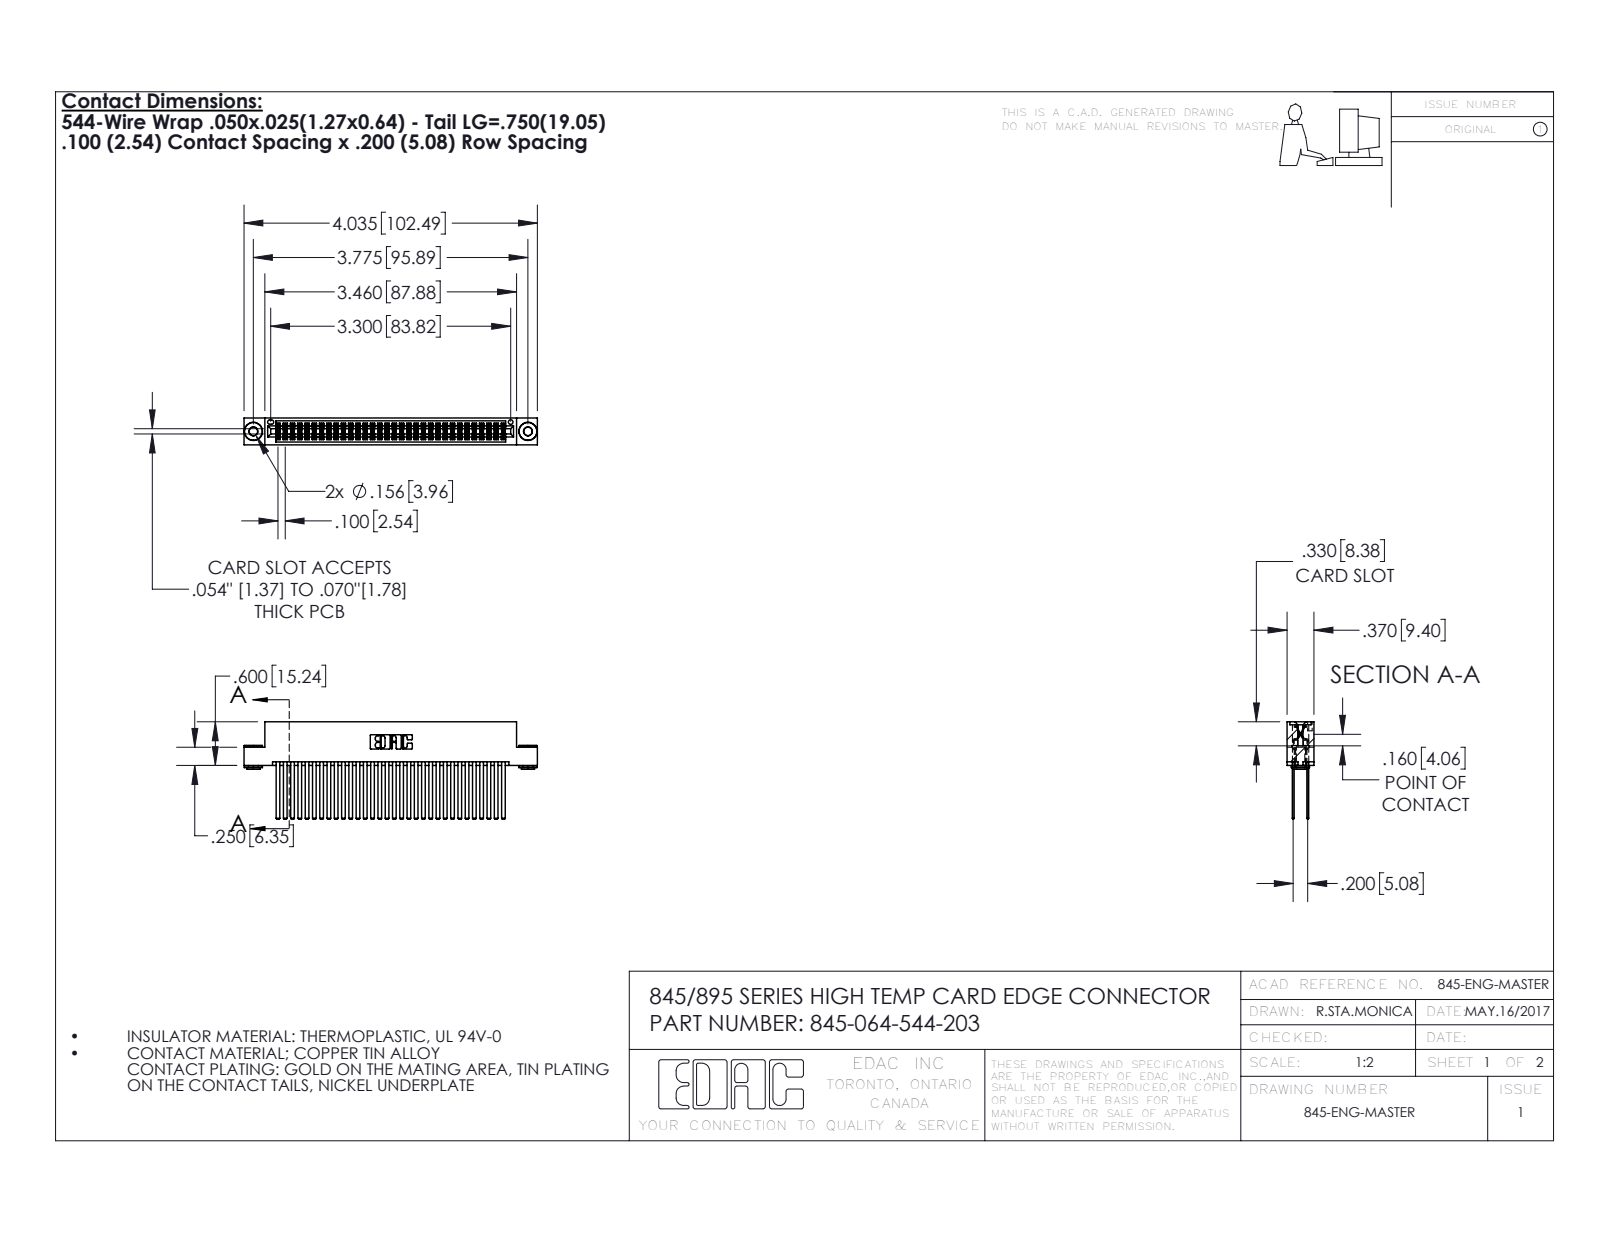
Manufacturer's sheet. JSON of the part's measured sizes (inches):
{"part_name": "345-064-544-203; 345-292-001_345-293-144; 345 Part_Flush Mounting Lugs - 0.156 Dia-TH; 345-250-002_345-250-002-102", "step_written_by": "SolidWorks 2016 (CONFIG_CONTROL_DESIGN)", "units": "inches", "bodies": {"solids": 67, "faces": 2980, "planar": 1946, "cylindrical": 1026, "other": 8}, "overall_size": [4.035, 1.337, 0.37], "volume_in3": 0.658, "surface_area_in2": 28.79, "round_holes": [[0.116, 2], [0.156, 2], [0.064, 1]], "round_bosses_or_shafts": [[0.25, 2], [0.18, 2], [0.136, 2]], "partial_cylinders_radius": [[0.006, 128], [0.01, 22], [0.007, 6], [0.031, 6], [0.026, 3], [0.014, 2], [0.019, 2], [0.022, 2]], "face_to_face_distances": [0.2, 0.025, 0.072, 0.098, 0.272, 0.298, 0.225, 0.175, 0.37, 0.05], "hole_center_spacings": [0.27, 3.54, 3.775]}
